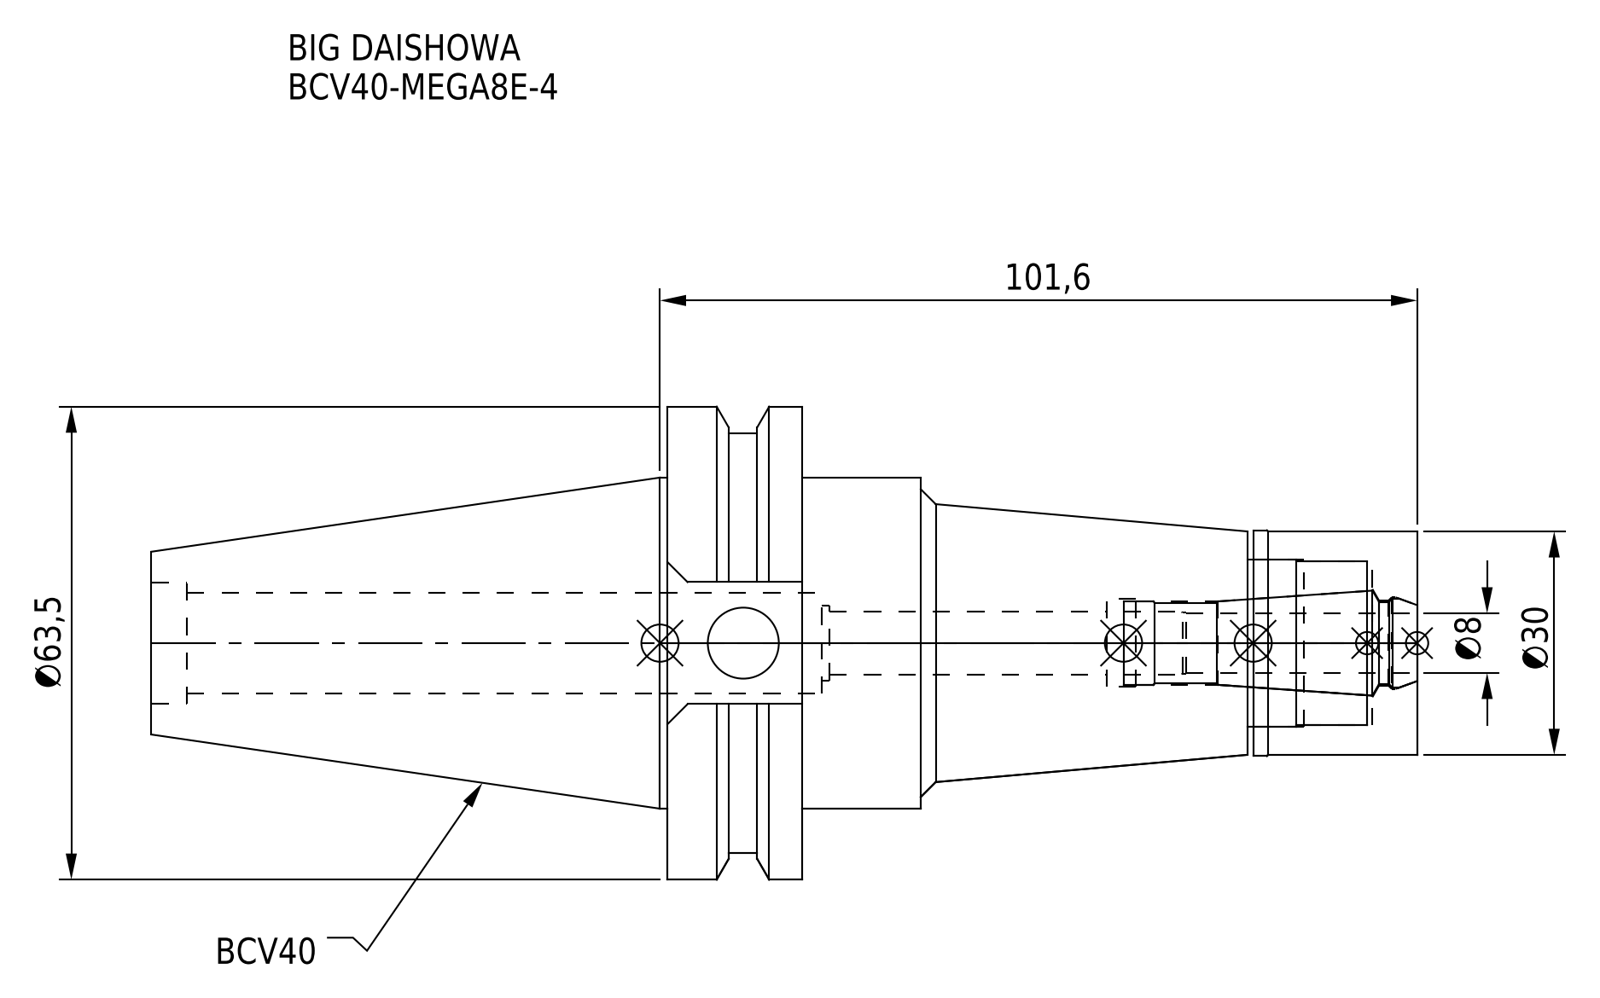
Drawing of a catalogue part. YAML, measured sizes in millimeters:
part_name: "BCV40-MEGA8E-4-080.stp; BCV40-MEGA8E-4-080-FreeParts; MEN8_1.stp; BCV40-MEGA8E-4_1.stp (+3 more)"
step_written_by: "SolidWorks 2019 (CONFIG_CONTROL_DESIGN)"
units: millimeters
bodies: {solids: 2, faces: 93, planar: 31, cylindrical: 42, other: 20}
overall_size: [169.85, 63.5, 61.35]
volume: 176747
surface_area: 35209
round_holes:
  - {diameter: 8.4, count: 1}
  - {diameter: 9.53, count: 1}
  - {diameter: 10, count: 1}
  - {diameter: 11.2, count: 1}
  - {diameter: 11.4, count: 1}
  - {diameter: 11.8, count: 1}
  - {diameter: 12.3, count: 1}
  - {diameter: 13.6, count: 1}
  - {diameter: 16.32, count: 1}
  - {diameter: 22, count: 1}
  - {diameter: 22.5, count: 1}
round_bosses_or_shafts:
  - {diameter: 63.5, count: 1}
  - {diameter: 56.36, count: 1}
  - {diameter: 44.45, count: 1}
  - {diameter: 30.3, count: 1}
  - {diameter: 30, count: 1}
face_to_face_distances: [18.05, 82.55, 100.6, 6, 22, 60.55, 78.6, 22.8, 0.8, 59.75]
